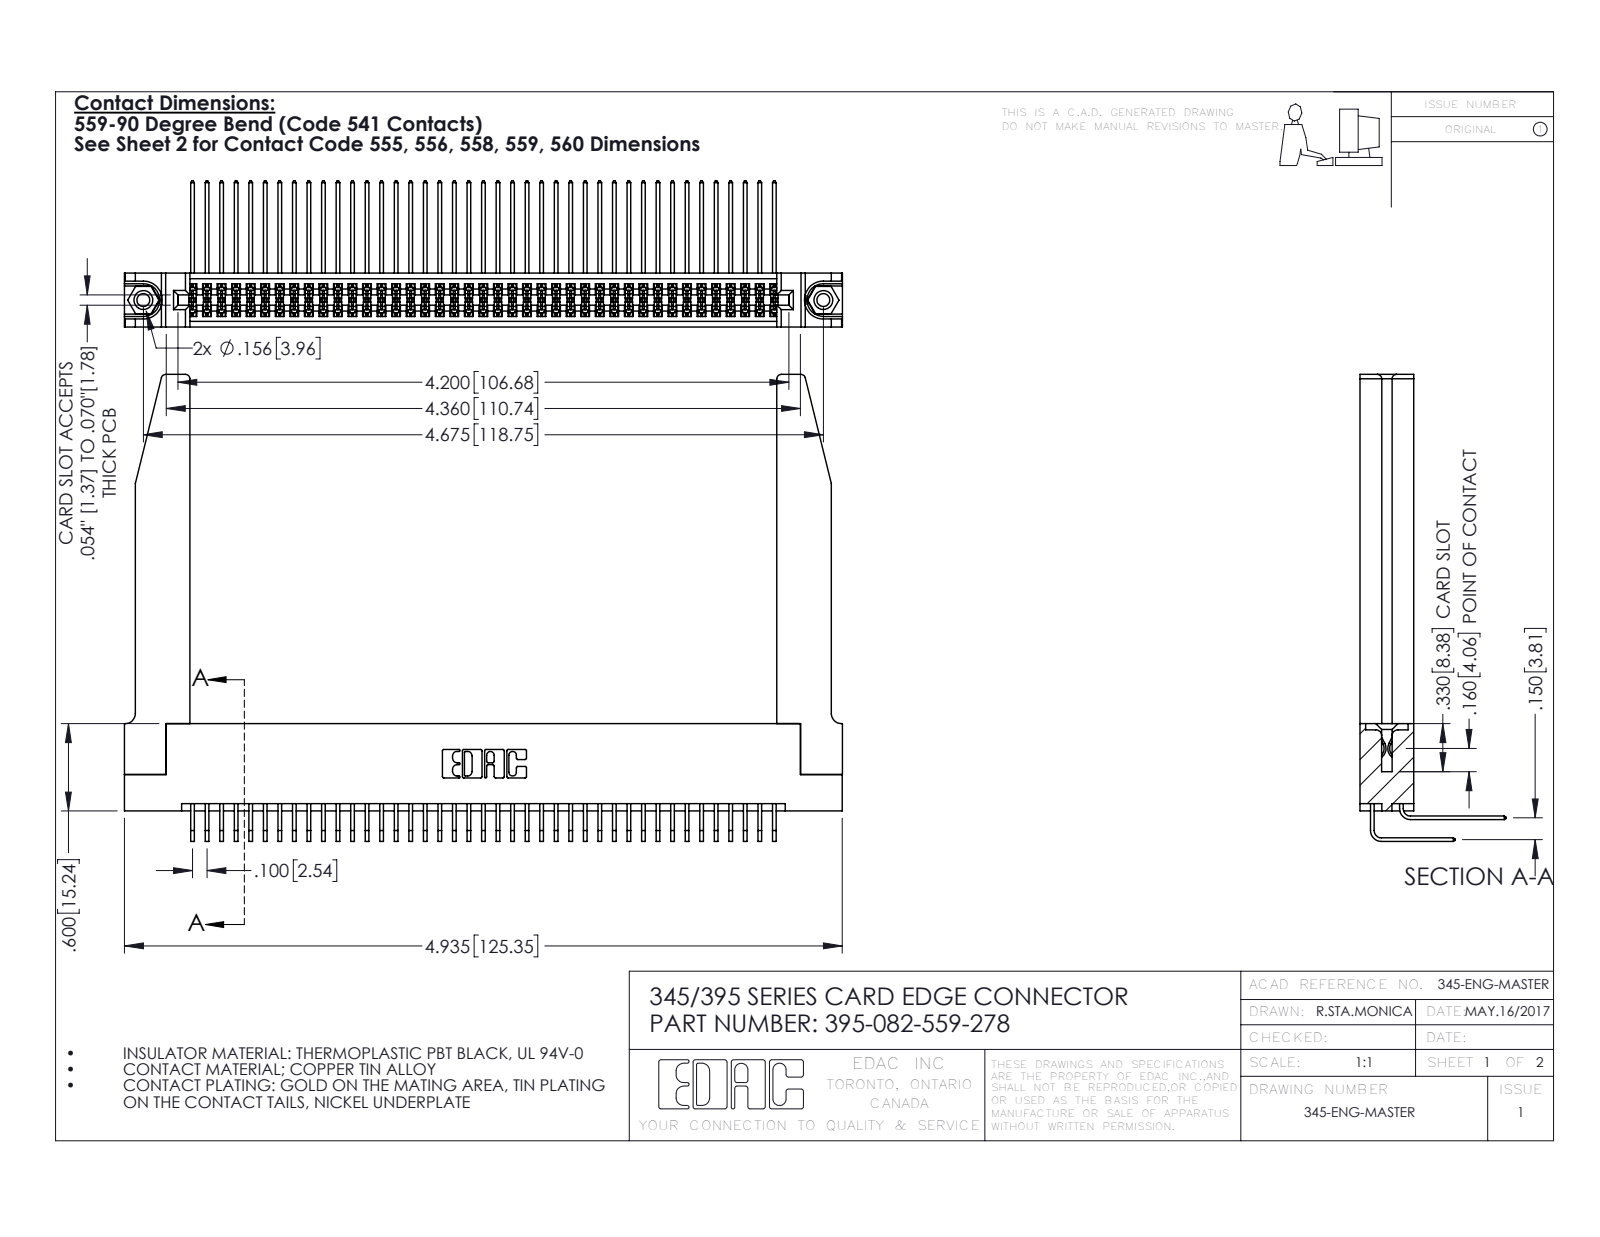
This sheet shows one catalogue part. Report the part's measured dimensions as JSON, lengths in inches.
{"part_name": "395-082-559-278; 345-292-001_558 559 Tail - 1; 345 Part_Flush Mounting Lugs - 0.156 Dia-TH; 345-250-001_345-250-001-102 (+2 more)", "step_written_by": "SolidWorks 2016 (CONFIG_CONTROL_DESIGN)", "units": "inches", "bodies": {"solids": 87, "faces": 4624, "planar": 3092, "cylindrical": 1480, "other": 52}, "overall_size": [4.936, 3.209, 1.005], "volume_in3": 1.246, "surface_area_in2": 42.98, "round_holes": [[0.089, 2], [0.125, 2], [0.156, 2], [0.064, 1]], "round_bosses_or_shafts": [[0.155, 2]], "partial_cylinders_radius": [[0.006, 123], [0.01, 22], [0.03, 8], [0.007, 6], [0.031, 6], [0.026, 3], [0.014, 2], [0.019, 2]], "face_to_face_distances": [0.37, 0.072, 0.298, 0.2, 0.098, 0.272, 0.025, 0.225, 0.175, 0.15], "hole_center_spacings": [0.27, 4.439, 4.675]}
